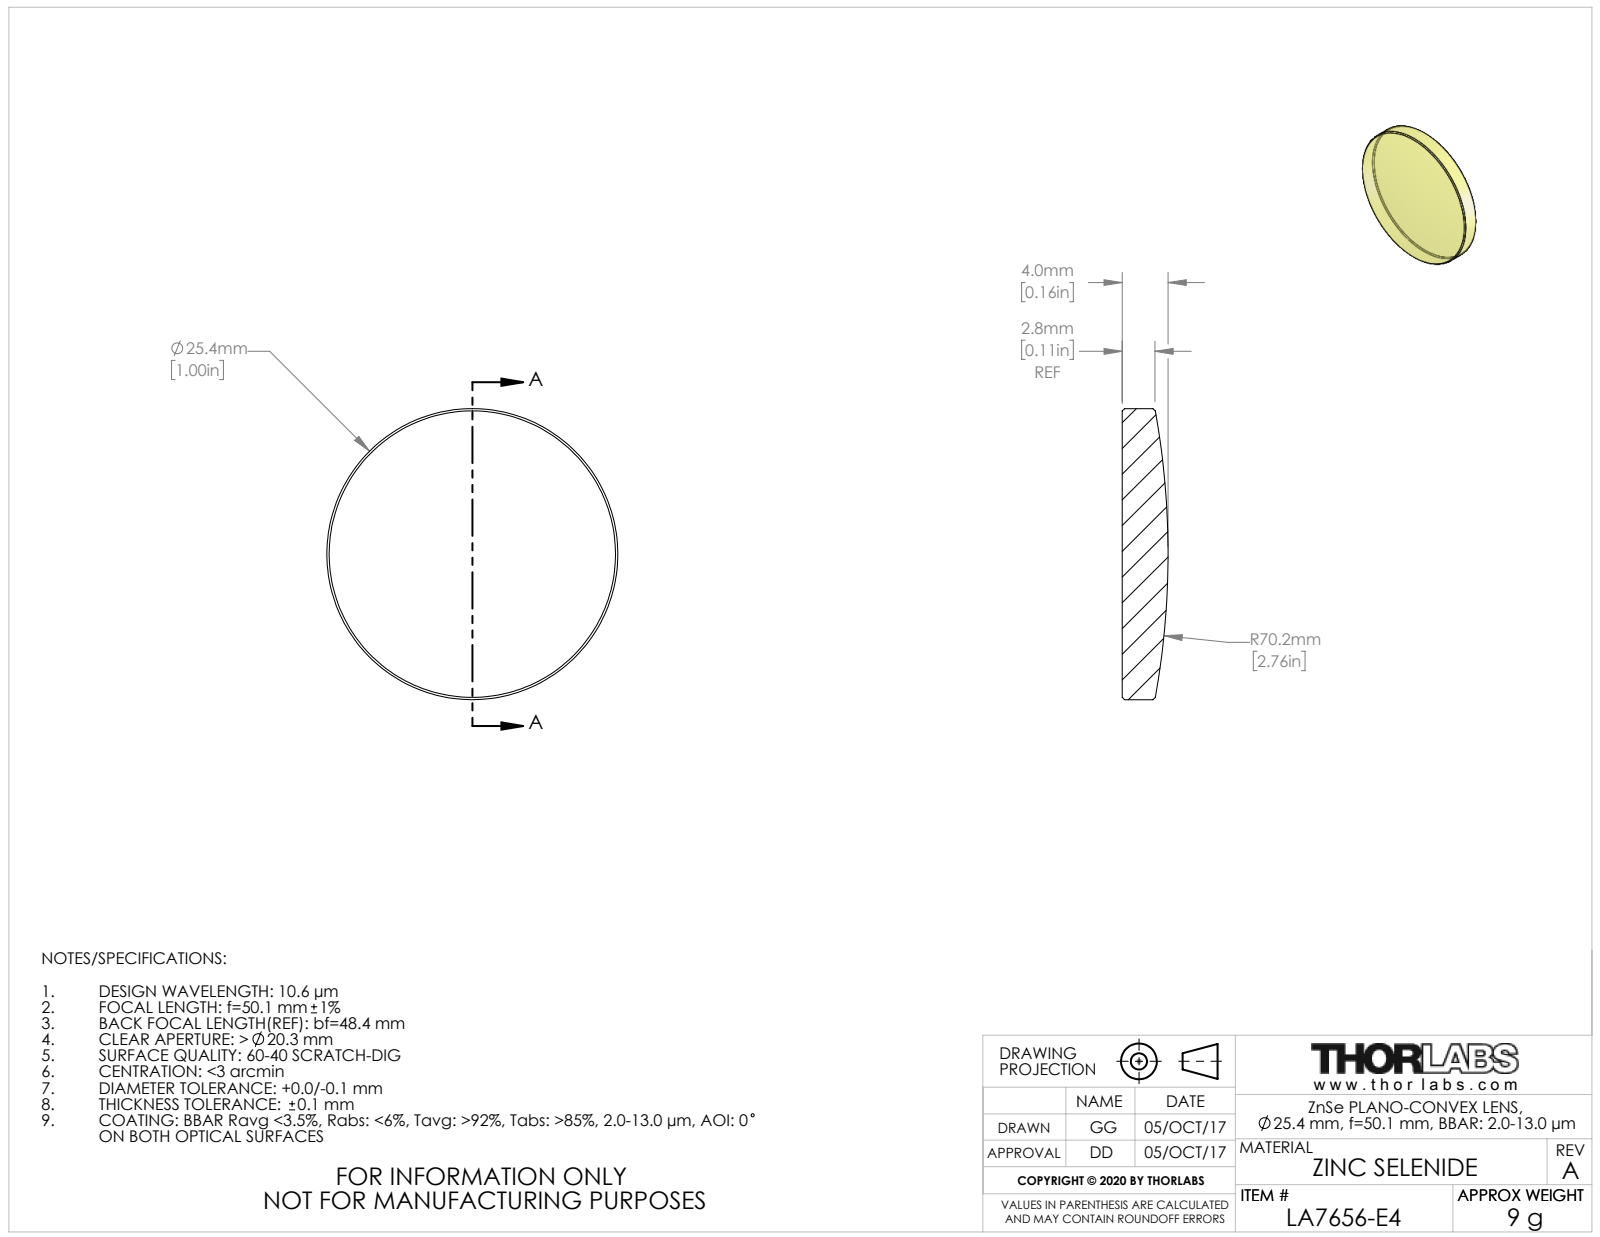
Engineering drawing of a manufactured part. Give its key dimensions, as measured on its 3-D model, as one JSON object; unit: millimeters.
{"part_name": "TTN098094-E0W", "step_written_by": "SolidWorks 2018 (CONFIG_CONTROL_DESIGN)", "units": "millimeters", "bodies": {"solids": 1, "faces": 9, "planar": 1, "cylindrical": 2, "other": 6}, "overall_size": [25.4, 25.4, 4], "volume_mm3": 1731, "surface_area_mm2": 1228, "round_bosses_or_shafts": [[25.4, 1]]}
